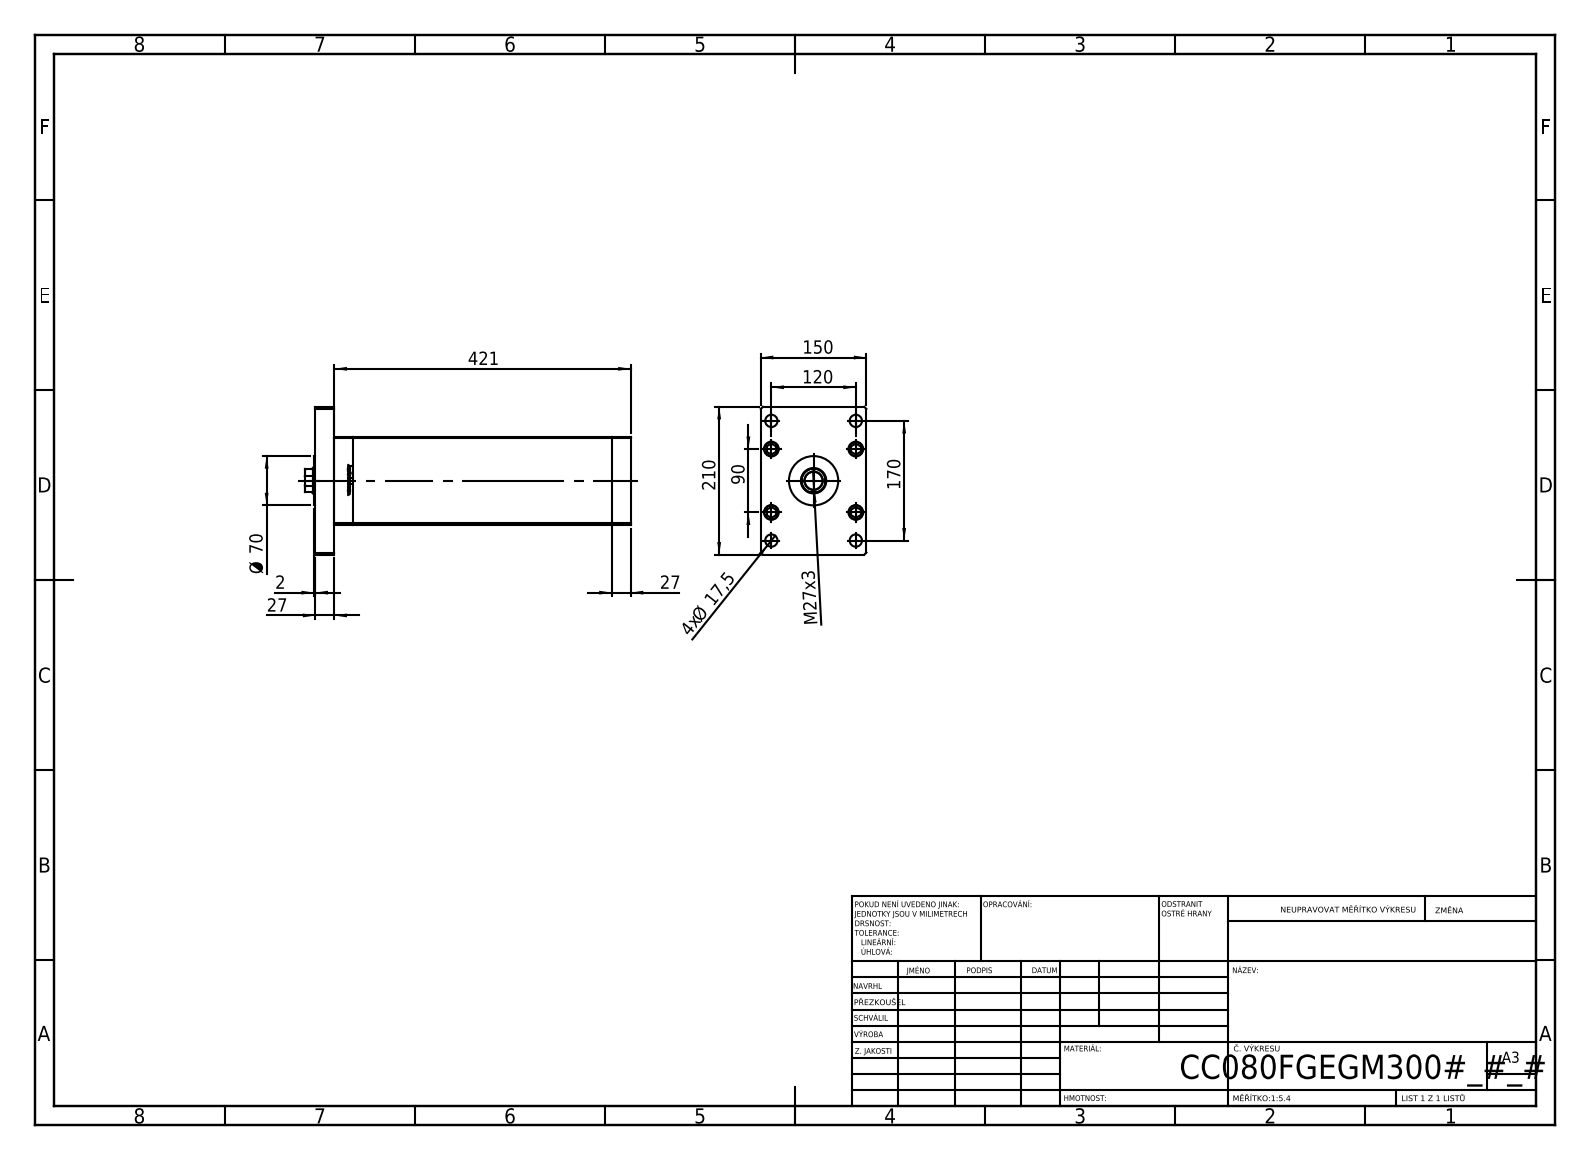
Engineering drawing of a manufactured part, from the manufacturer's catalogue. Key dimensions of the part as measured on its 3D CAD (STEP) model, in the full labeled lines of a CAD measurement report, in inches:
Part name (STEP PRODUCT): V220C_F; V220C_F_MIDDLE; V220C BACK_F; V220C_FRONT_F (+2 more)
STEP written by: SolidWorks 2019 (CONFIG_CONTROL_DESIGN)
Units: inches
Bodies: 19 solids, 1310 faces (517 planar, 187 cylindrical, 606 other)
Overall size (bounding box): 18.228 × 8.268 × 5.906
Volume: 443.7 in³ · Surface area: 1 021 in²
Round holes (diameter × count): ⌀0.689 ×9, ⌀0.866 ×5, ⌀0.63 ×4, ⌀0.827 ×4, ⌀0.079 ×2, ⌀0.518 ×2, ⌀1.004 ×1, ⌀1.417 ×1, ⌀1.476 ×1
Round bosses / shafts (diameter × count): ⌀0.315 ×9, ⌀0.827 ×5, ⌀3.15 ×1, ⌀2.756 ×1
Partial cylindrical surfaces — rounded edges, fillets, slot ends (radius × count): R0.037 ×2, R0.689 ×1
Main face-to-face distances: 1.063, 5.906, 4.921, 15.512, 16.575, 14.449, 2.126, 17.638, 1.319, 0.256
Hole centre spacings: 2.008, 1.575, 2.953, 4.096, 4.724, 4.98, 5.118, 6.965
